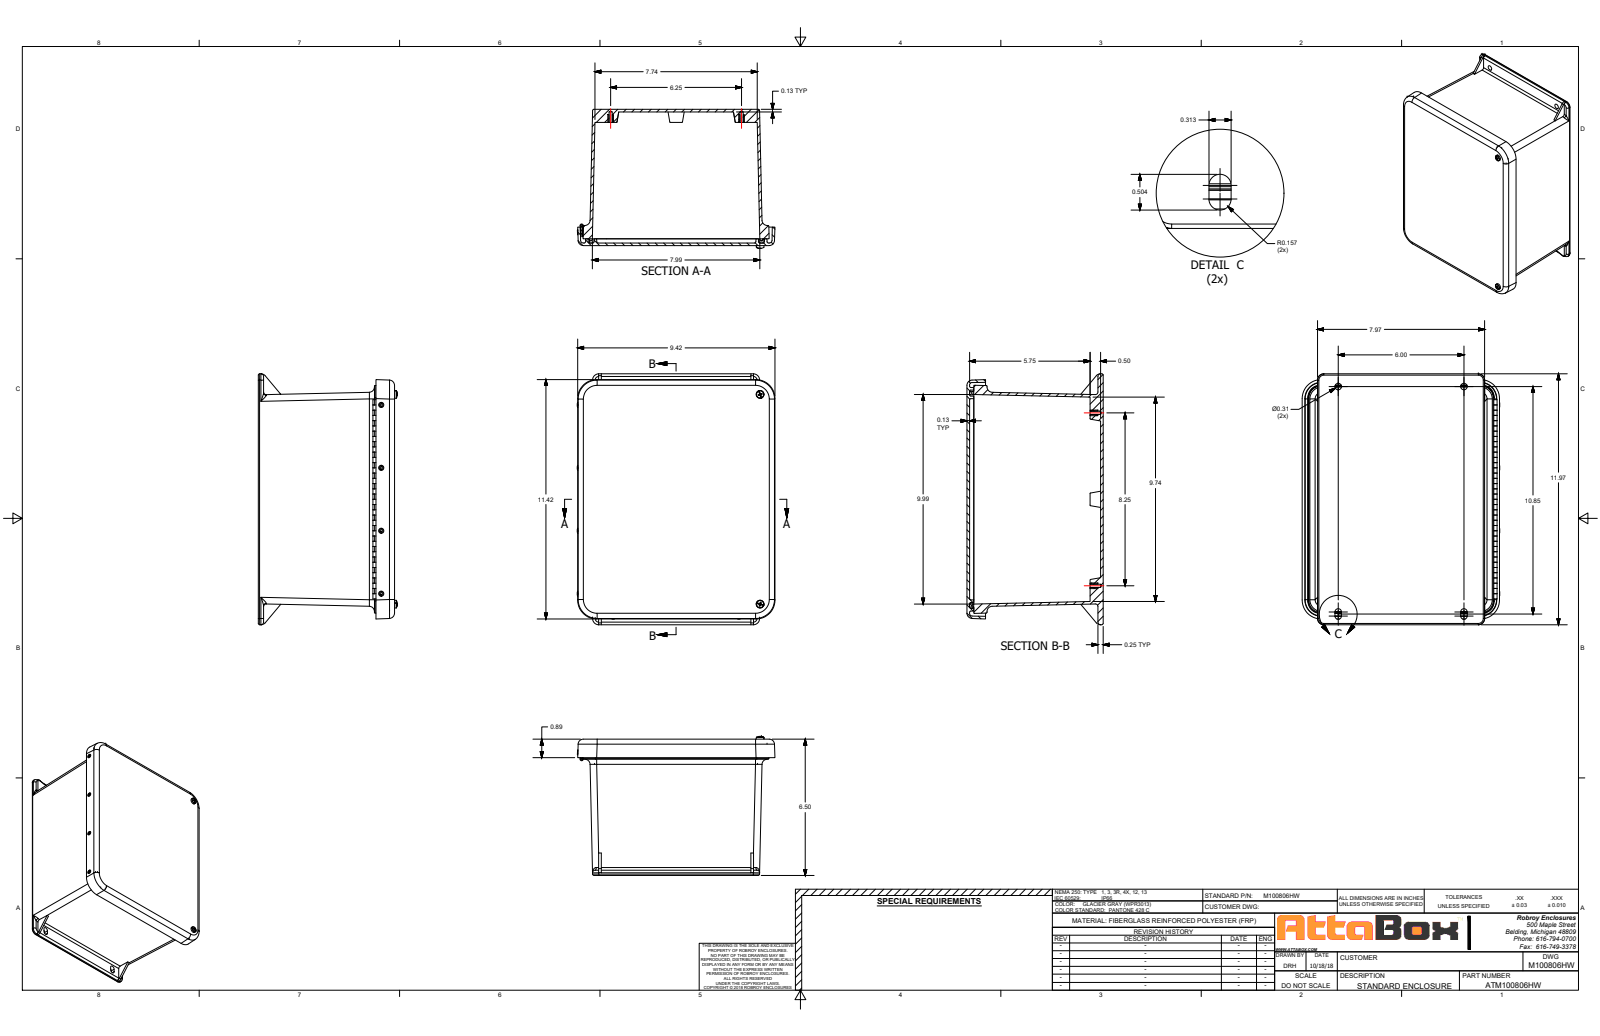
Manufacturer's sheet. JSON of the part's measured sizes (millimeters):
{"part_name": "M100806HW", "step_written_by": "SolidWorks 2018 (AUTOMOTIVE_DESIGN)", "units": "millimeters", "bodies": {"solids": 30, "faces": 1184, "planar": 397, "cylindrical": 439, "other": 348}, "overall_size": [303.9, 240, 168.4], "volume_mm3": 1253000, "surface_area_mm2": 654200, "round_holes": [[3.9, 12], [4, 12], [2.6, 8], [3.3, 8], [3.6, 8], [9.5, 4], [8, 2], [2.2, 1]], "round_bosses_or_shafts": [[6.9, 12], [3.2, 5], [3.2, 3], [4.8, 2], [4, 2], [3.9, 1], [3.9, 1]], "partial_cylinders_radius": [[0.8, 26], [1.6, 22], [1.6, 20], [3.2, 18], [1, 16], [1.6, 14], [7.6, 12], [6.4, 10]], "face_to_face_distances": [3.2, 165.1, 3.1, 3.1, 161.9, 158.7, 3.2, 161.9, 156.8, 153.6], "hole_center_spacings": [152.4, 76.2, 63.5, 88.9, 215.9, 228.6, 221.1, 27.1]}
